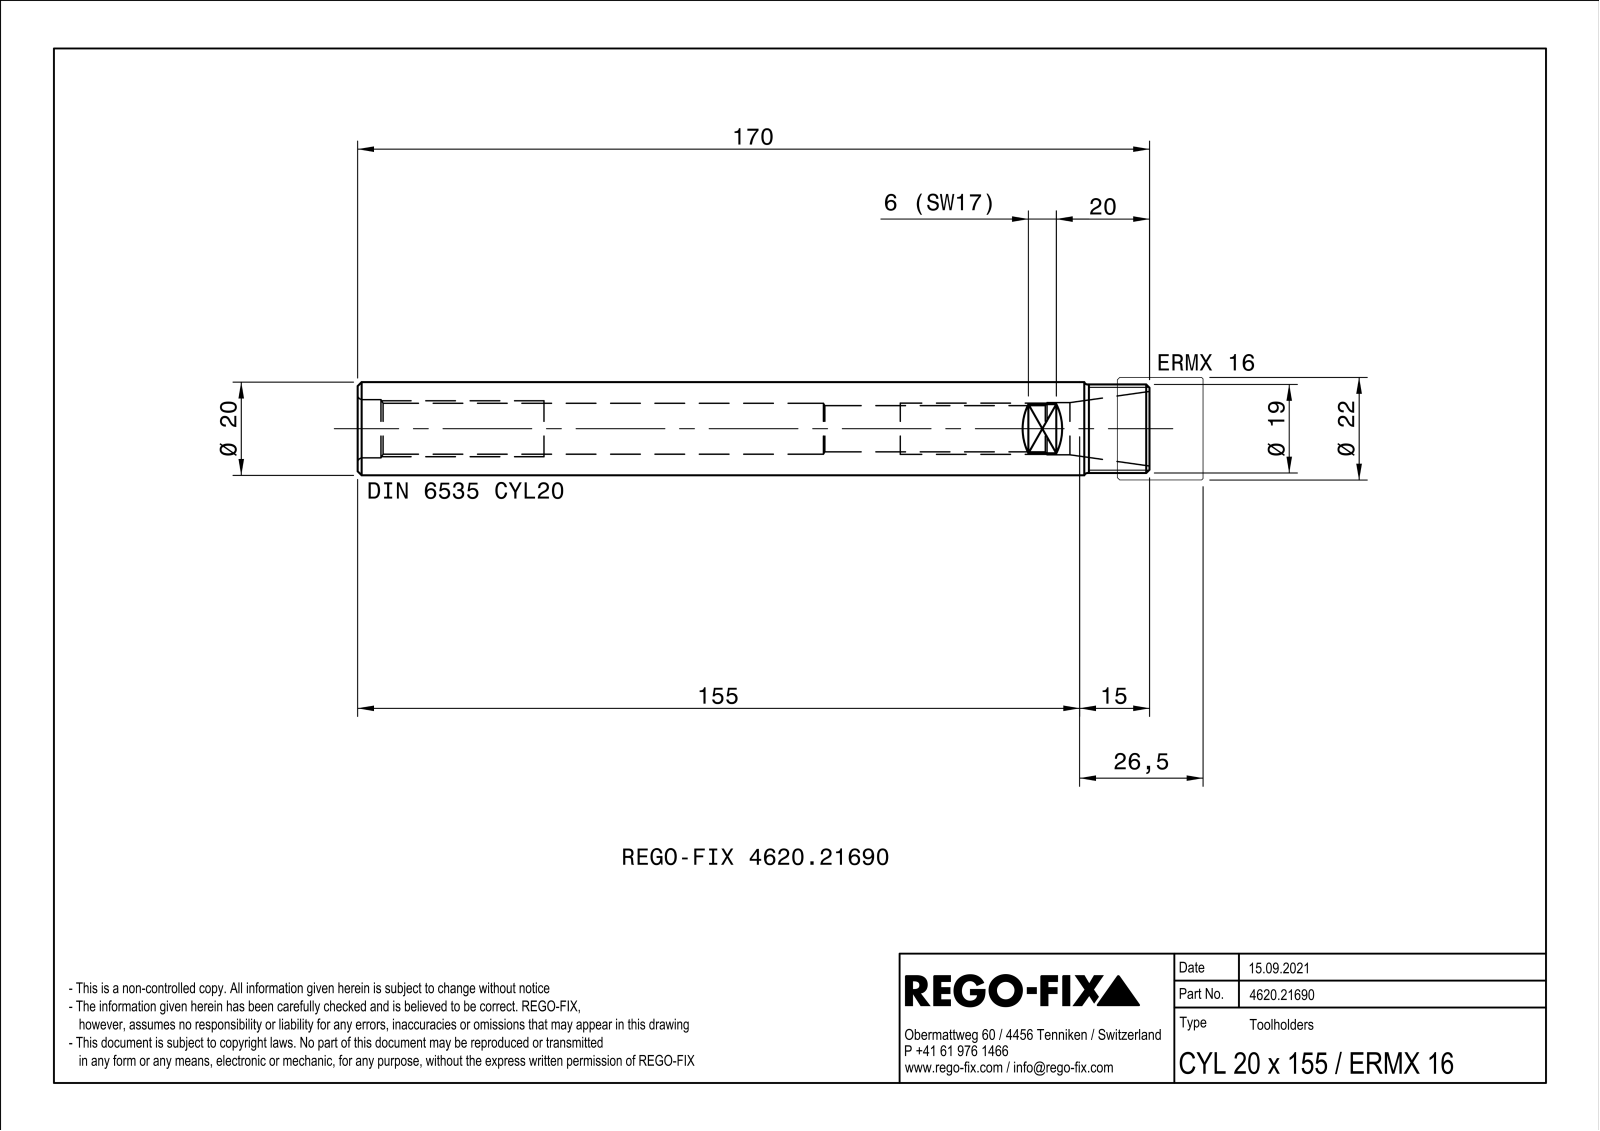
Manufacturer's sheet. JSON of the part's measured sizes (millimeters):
{"part_name": "NOCUT", "step_written_by": "SIEMENS PLM Software Solid Edge ST10 (AUTOMOTIVE_DESIGN)", "units": "millimeters", "bodies": {"solids": 2, "faces": 51, "planar": 16, "cylindrical": 17, "other": 18}, "overall_size": [170.2, 20.3, 20.3], "volume_mm3": 74850, "surface_area_mm2": 33690, "round_holes": [[9.92, 1], [10.92, 1], [11.2, 1], [12.5, 1]], "round_bosses_or_shafts": [[20.3, 1], [20, 1], [19.3, 1], [19, 1]], "face_to_face_distances": [17, 7.78, 170.2, 170]}
